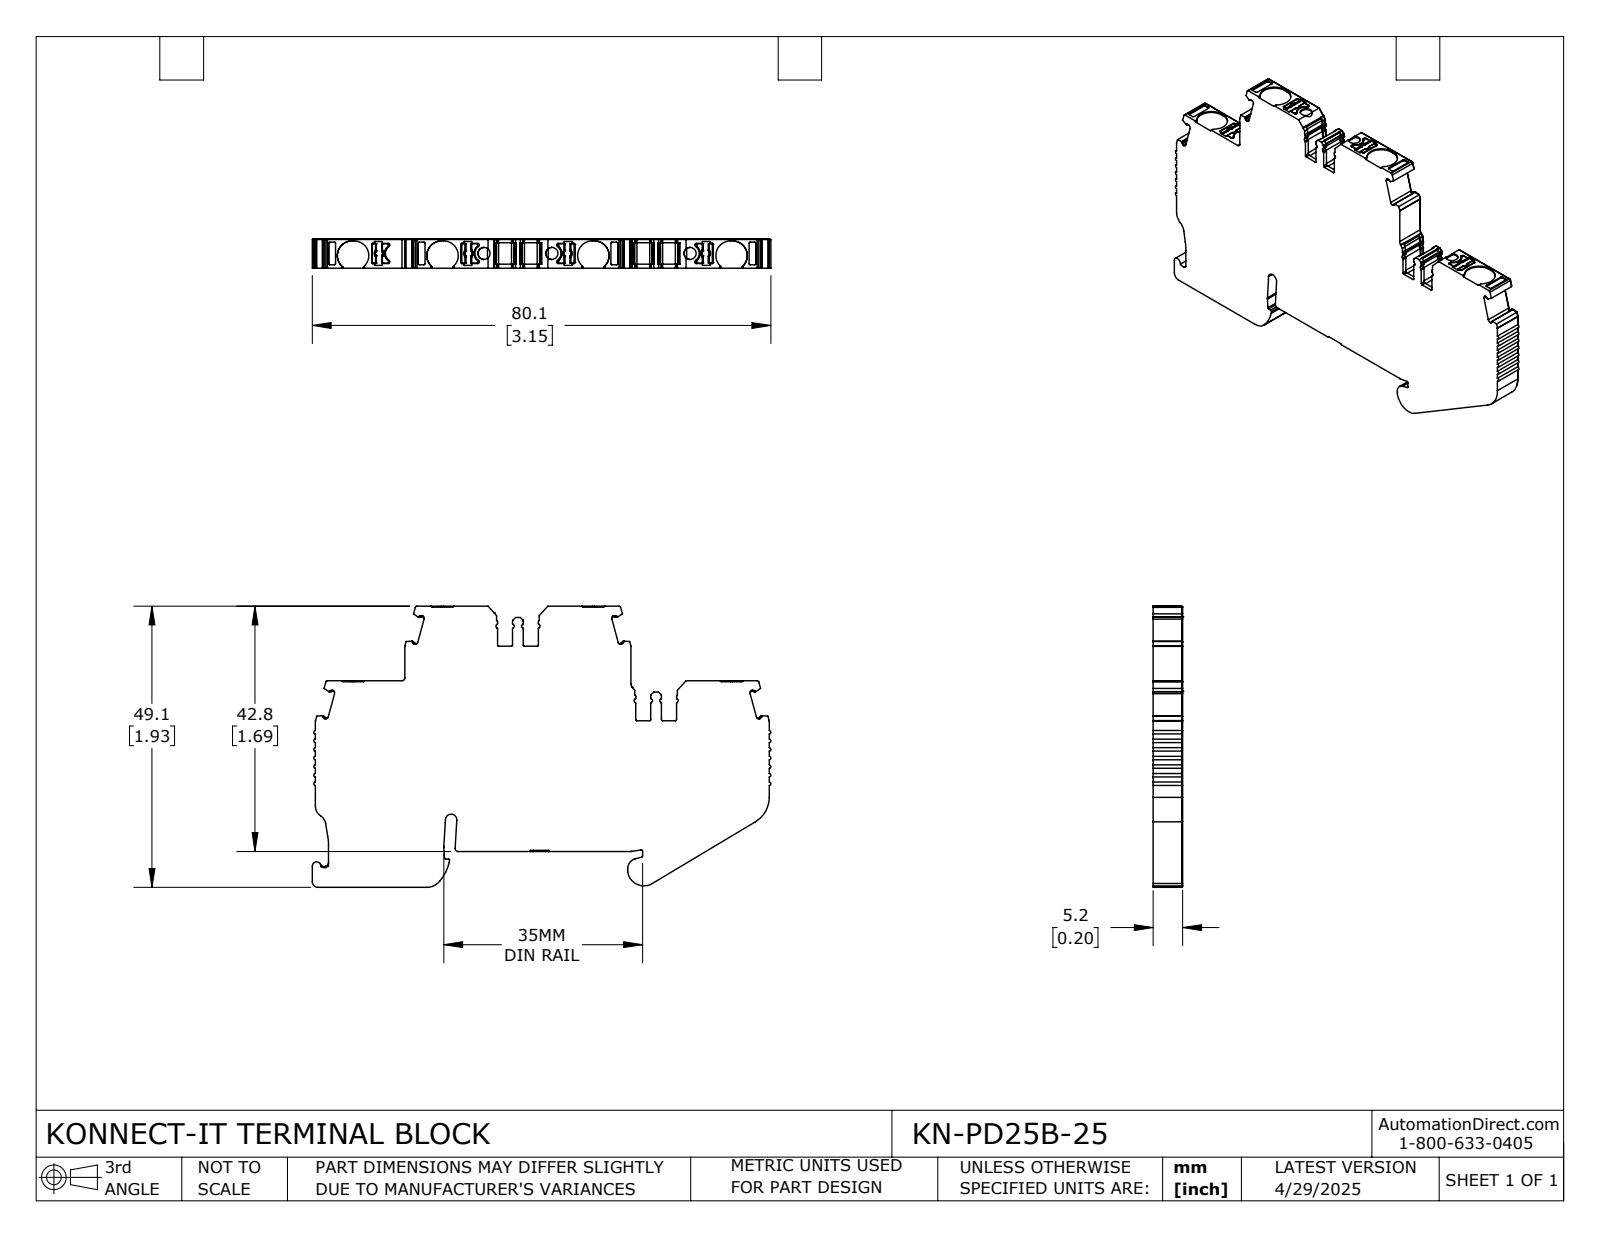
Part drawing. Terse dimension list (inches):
name: KN-PD25B-25
written by: SolidWorks 2024 (CONFIG_CONTROL_DESIGN)
unit: in
bodies: 1 solid, 977 faces (472 planar, 438 cylindrical, 67 other)
size: 3.153 × 1.933 × 0.203
volume: 0.889 in³; area: 11.63 in²
holes: 3× ⌀0.083
rounds: 100× R0.008, 57× R0.012, 41× R0.004, 21× R0.02, 17× R0.016, 16× R0.006, 9× R0.024, 8× R0.006
face distances: 0.203, 0.512, 0.246, 1.678, 1.166, 1.924, 0.079, 1.412, 0.504, 0.95
hole spacings: 0.466, 0.95, 1.417
